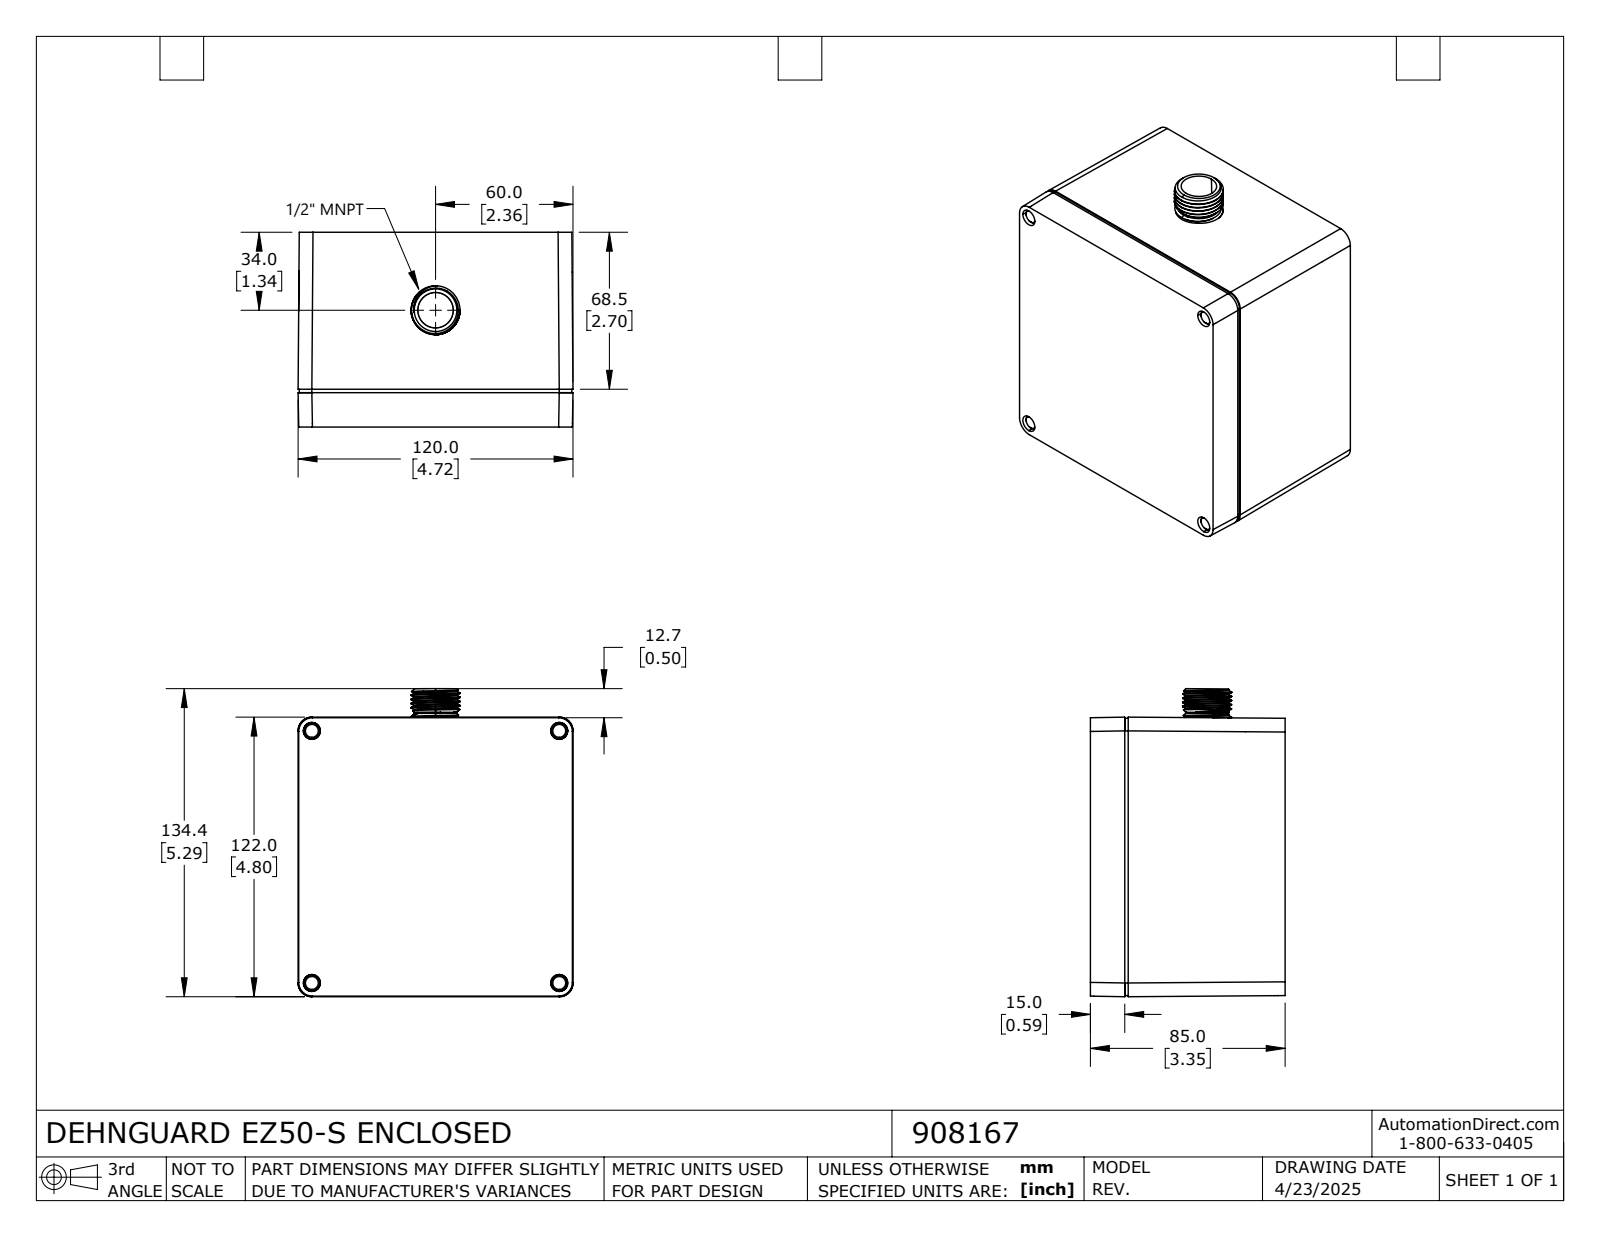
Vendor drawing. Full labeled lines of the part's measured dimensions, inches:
Part name (STEP PRODUCT): 908167
STEP written by: SolidWorks 2024 (AUTOMOTIVE_DESIGN)
Units: inches
Bodies: 2 solids, 610 faces (378 planar, 162 cylindrical, 70 other)
Overall size (bounding box): 5.293 × 4.724 × 3.346
Volume: 38.55 in³ · Surface area: 297.7 in²
Round holes (diameter × count): ⌀0.165 ×4, ⌀0.315 ×4
Round bosses / shafts (diameter × count): ⌀0.276 ×6, ⌀0.113 ×4, ⌀1.166 ×1, ⌀1.125 ×1, ⌀1.026 ×1, ⌀0.84 ×1
Partial cylindrical surfaces — rounded edges, fillets, slot ends (radius × count): R0.004 ×8, R0.236 ×8, R0.217 ×4, R0.012 ×3, R0.02 ×3, R0.03 ×2, R0.079 ×2, R3.937 ×2
Main face-to-face distances: 0.118, 0.157, 3.346, 3.189, 3.228, 3.071, 0.12, 0.039, 0.37, 0.119
Hole centre spacings: 3.543, 4.331, 5.596
